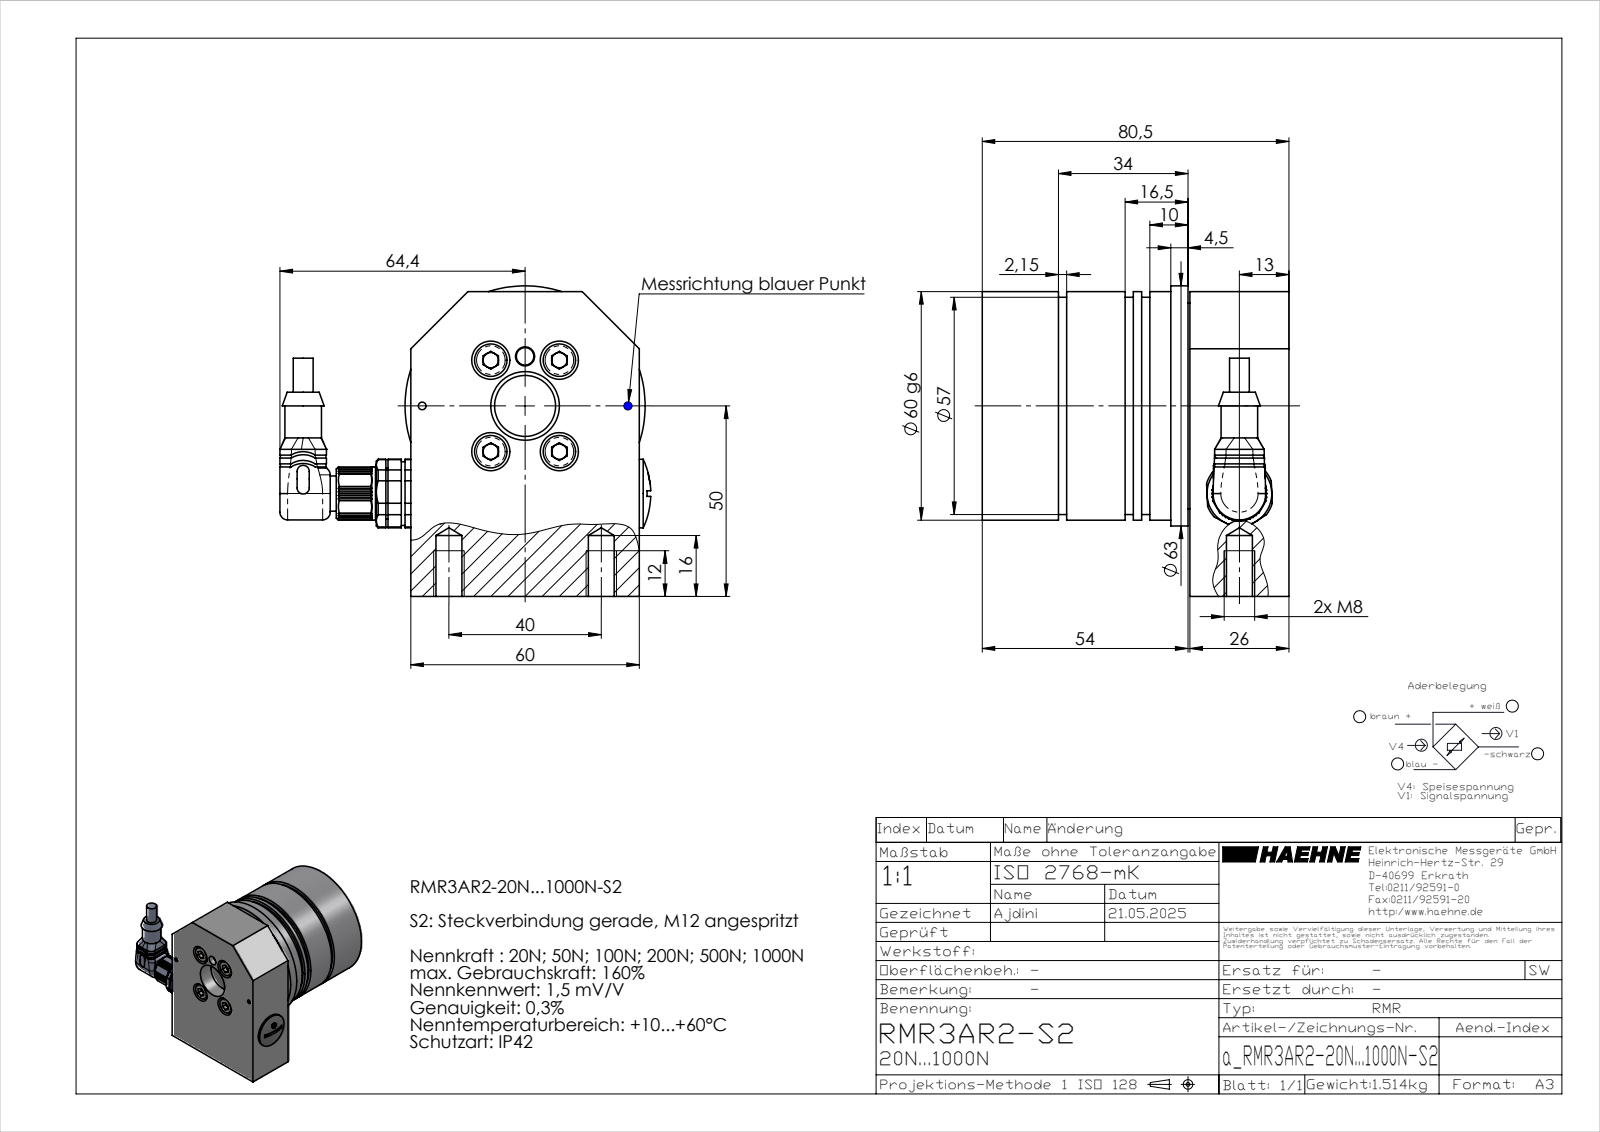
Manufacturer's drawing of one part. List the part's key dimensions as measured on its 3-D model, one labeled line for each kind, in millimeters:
Part name (STEP PRODUCT): a_RMR3AR2-20N...1000N-S2
STEP written by: SolidWorks 2023 (AUTOMOTIVE_DESIGN)
Units: millimetres
Bodies: 15 solids, 974 faces (533 planar, 248 cylindrical, 193 other)
Overall size (bounding box): 97.34 × 81.5 × 80.5
Volume: 235 738 mm³ · Surface area: 73 396 mm²
Round holes (diameter × count): ⌀1.1 ×4, ⌀1.15 ×4, ⌀1.6 ×4, ⌀1.85 ×4, ⌀4.2 ×4, ⌀5.3 ×4, ⌀10 ×4, ⌀2 ×2, ⌀6.8 ×2, ⌀0.64 ×1, ⌀1.2 ×1, ⌀3 ×1
Round bosses / shafts (diameter × count): ⌀0.86 ×5, ⌀8.5 ×4, ⌀5 ×4, ⌀1.8 ×4, ⌀1.55 ×4, ⌀1.5 ×4, ⌀1 ×4, ⌀63 ×1
Partial cylindrical surfaces — rounded edges, fillets, slot ends (radius × count): R0.2 ×16, R0.3 ×9, R0.4 ×4, R0.53 ×4, R1 ×4, R1.27 ×4, R6 ×4, R1.6 ×2
Main face-to-face distances: 11.5, 48.5, 37, 73, 54.5, 62, 11, 47, 15, 26
Hole centre spacings: 2.5, 3.54, 15, 21.63, 37.95, 5, 9.06, 18
